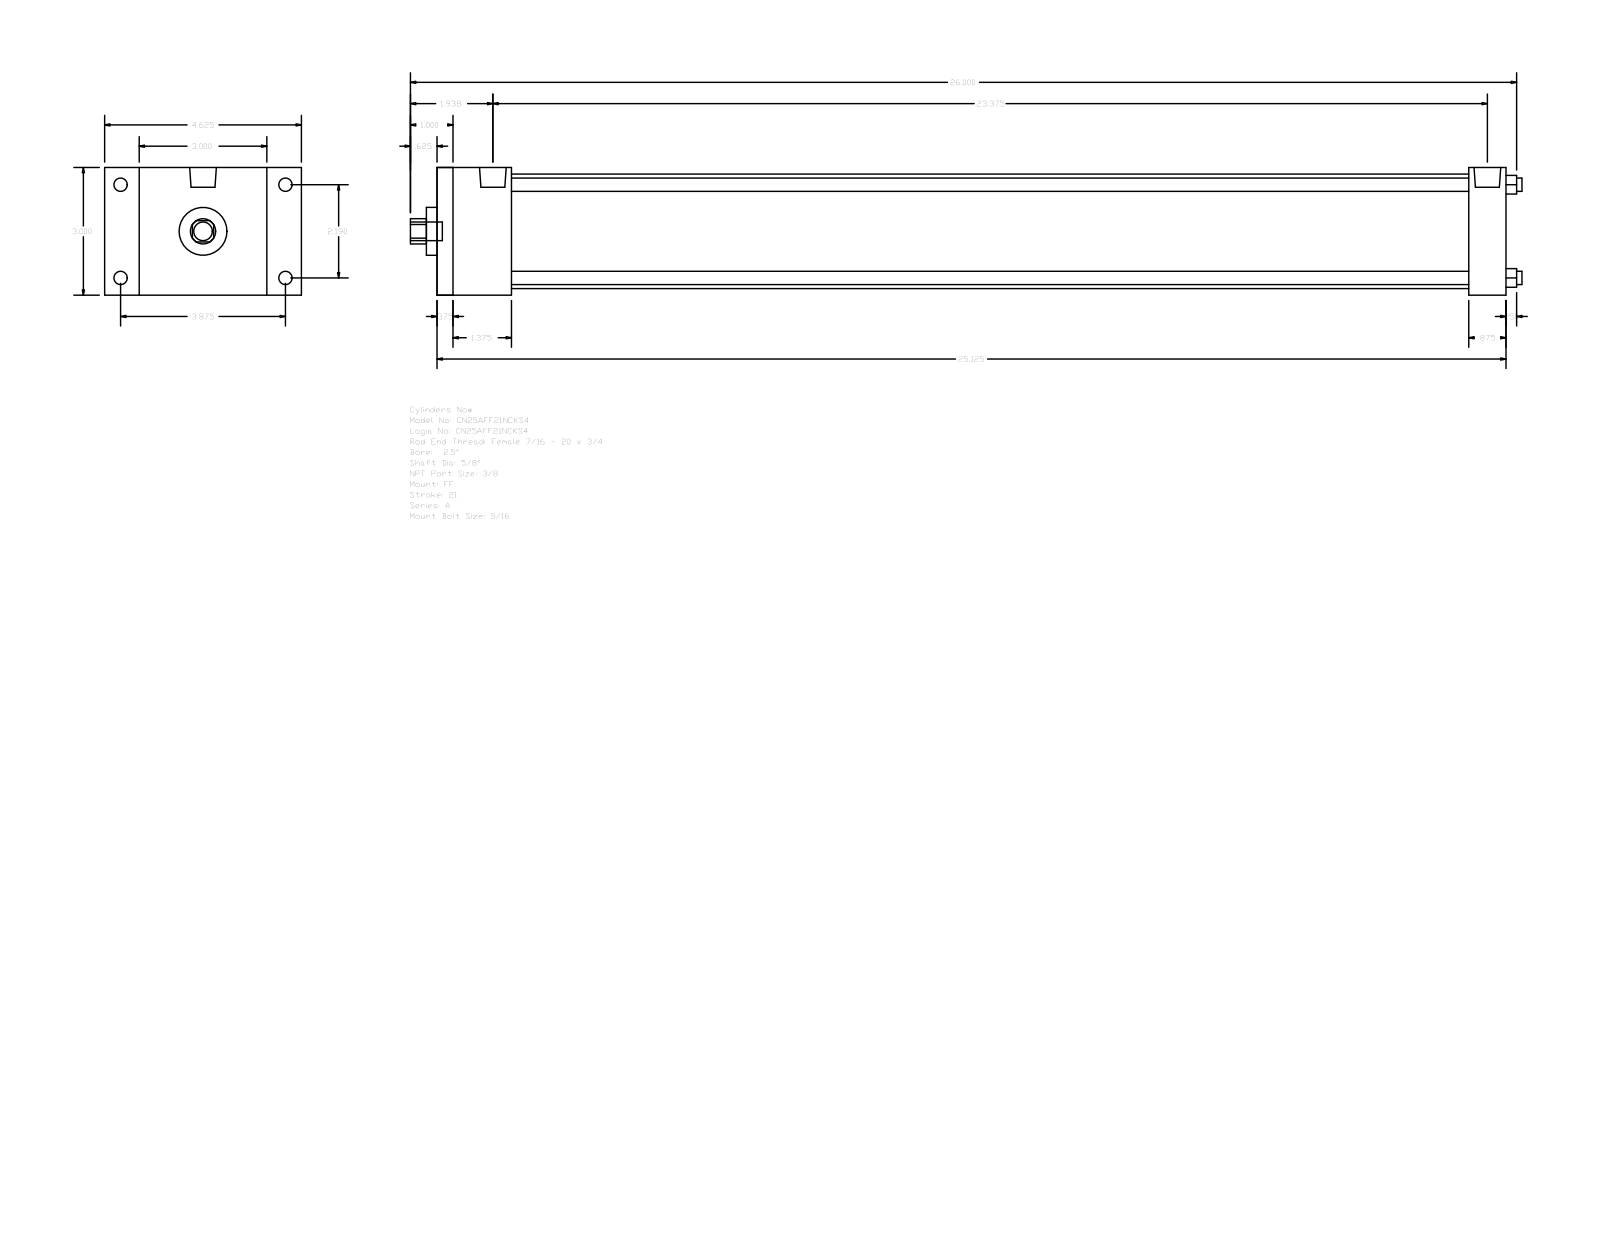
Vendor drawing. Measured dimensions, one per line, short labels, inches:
name: A_FF__0250_0.625
written by: GSSL Pune (CONFIG_CONTROL_DESIGN)
unit: in
bodies: 0 solids, 92 faces (64 planar, 28 cylindrical, 0 other)
size: 26.125 × 4.625 × 3
holes: 4× ⌀0.313, 1× ⌀0.625, 1× ⌀1.125, 1× ⌀2.69
bosses: 4× ⌀0.313, 4× ⌀0.219, 2× ⌀0.627, 1× ⌀0.437
rounds: 1× R0.297
face distances: 3, 25.125, 0.375, 24.75, 1.75, 24.25, 1.375, 23.875, 22.5, 23.375
hole spacings: 1.548, 2.19, 3.097
